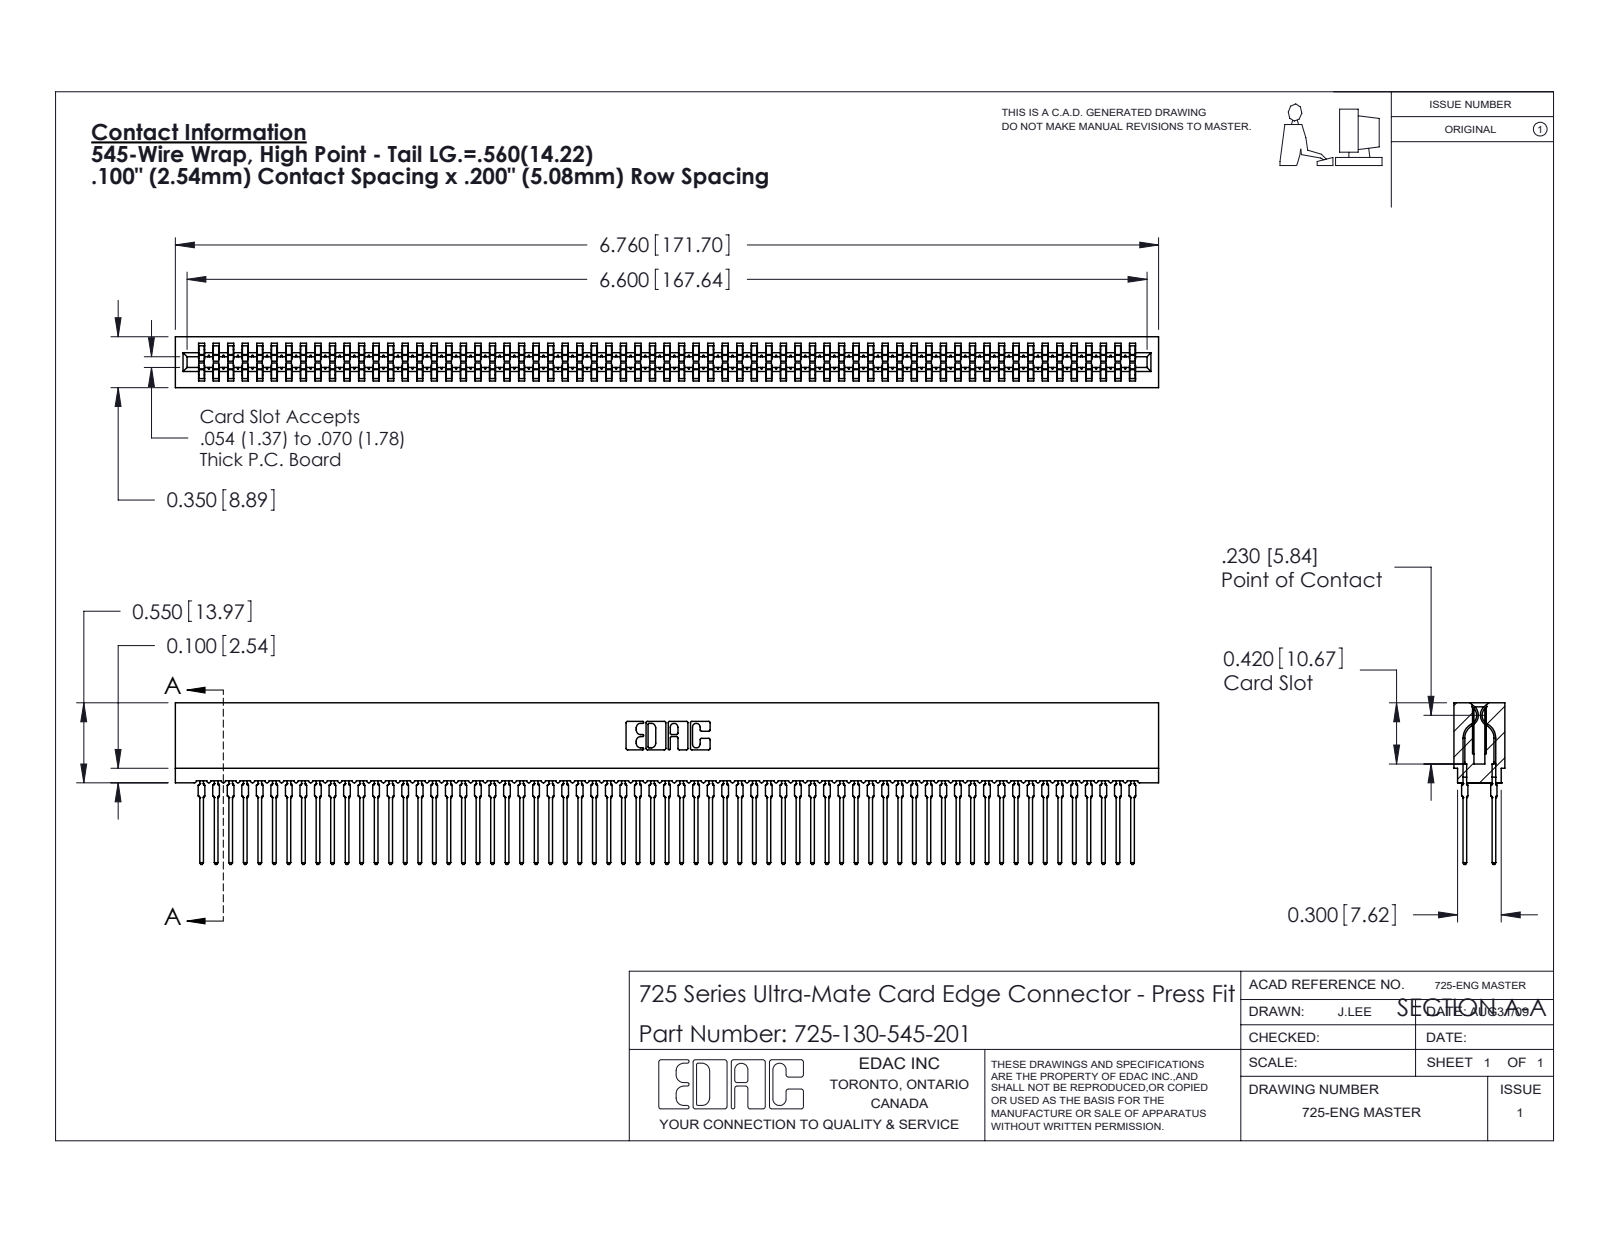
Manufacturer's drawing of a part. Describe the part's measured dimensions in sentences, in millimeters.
The part is named "725-130-545-201; 745-292-001_545; 725 Part_Insulator Option - 01". Its 3-D file was written by "SolidWorks 2020 (CONFIG_CONTROL_DESIGN)". It is 131 solids with 11730 faces: 6035 planar, 2315 cylindrical and 3380 other. Overall it measures 171.7 by 28.2 by 8.9 millimeters. Its volume is 14 000 cubic millimeters and its surface area 31 950 square millimeters. Partial cylindrical surfaces (rounded edges, fillets, slot ends): 260 of radius 0.5, 130 of radius 0.4, 22 of radius 0.3, 8 of radius 0.1, 8 of radius 0.3, 6 of radius 0.2, 6 of radius 0.8, 3 of radius 0.7. The main face-to-face distances are 1.6, 7.3, 5.1, 8.9, 5.4, 3.5, 1.9, 3.8, 2.2, 6.7.
